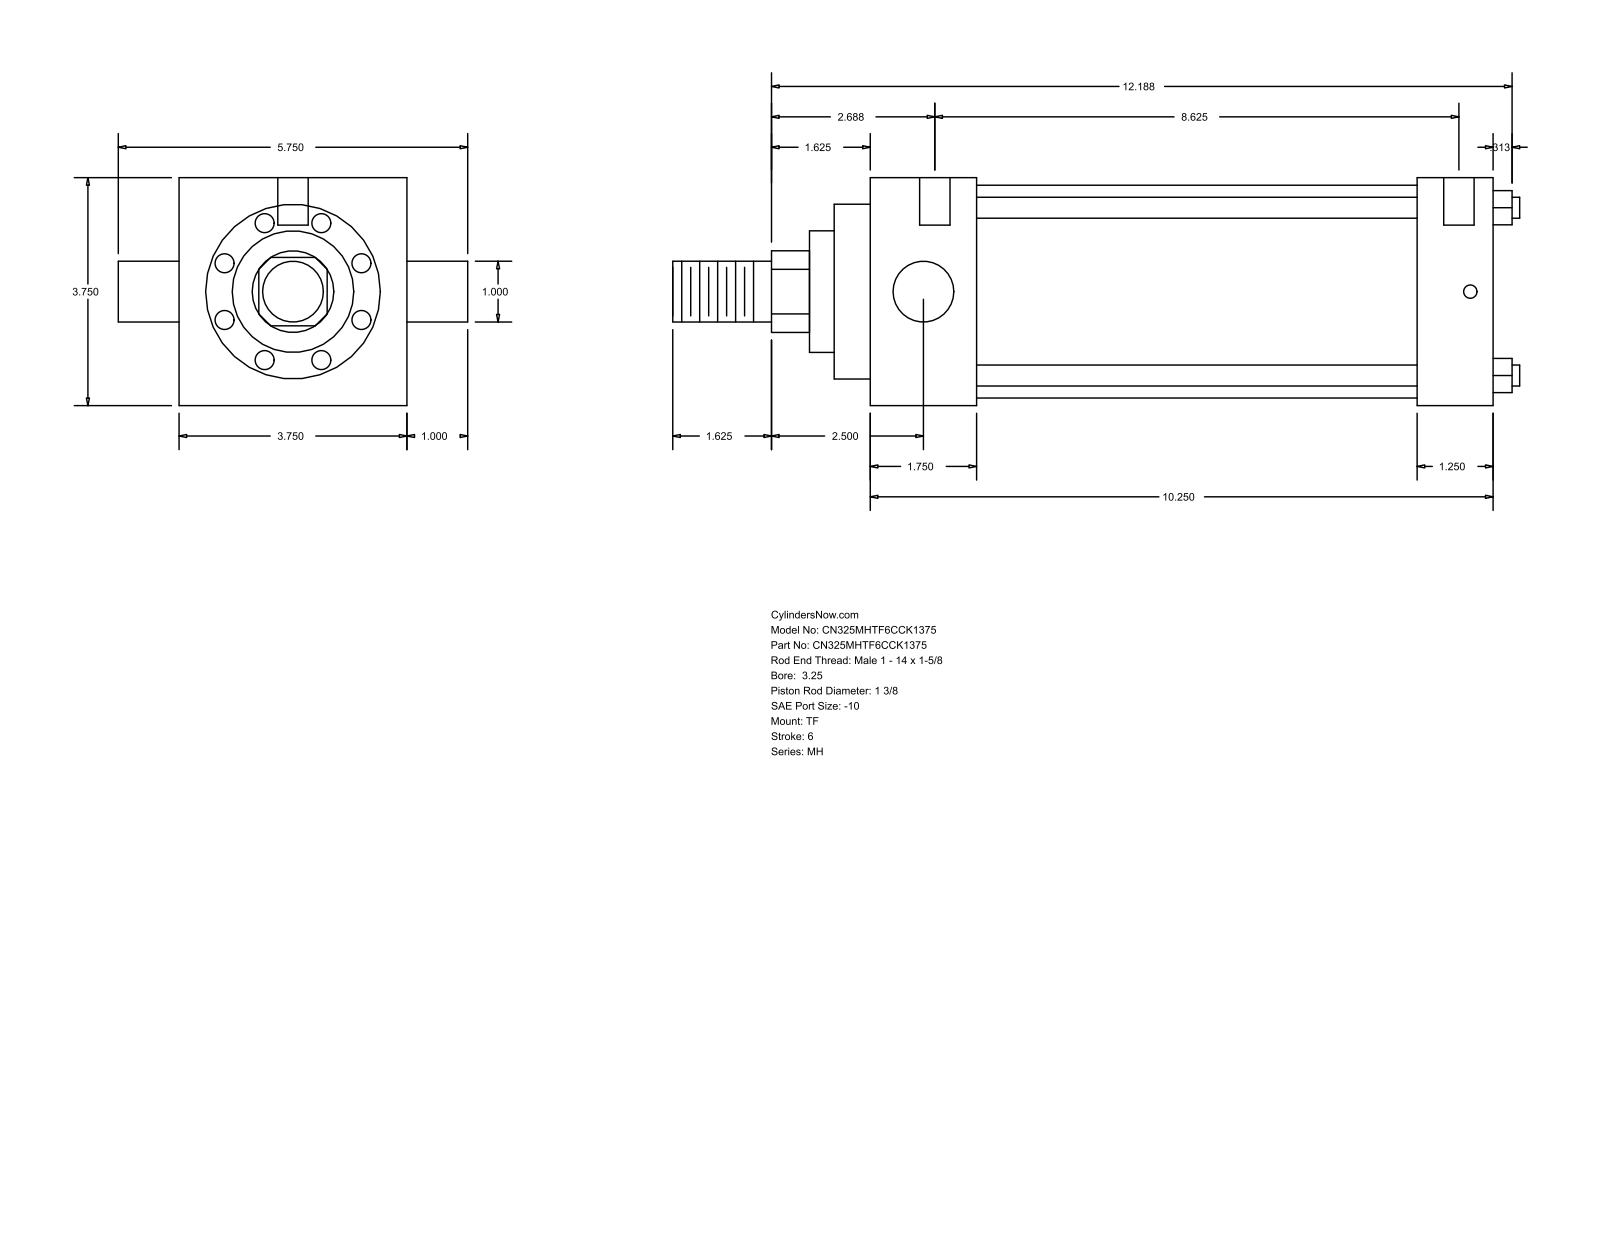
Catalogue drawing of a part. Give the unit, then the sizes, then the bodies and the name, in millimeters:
Units: millimetres
Overall size (bounding box): 354.01 × 146.05 × 95.25
Round holes (diameter × count): ⌀5.56 ×3, ⌀12.7 ×2
Round bosses / shafts (diameter × count): ⌀8.76 ×4, ⌀25.4 ×2, ⌀88.9 ×1, ⌀73.03 ×1, ⌀50.8 ×1, ⌀34.92 ×1
Partial cylindrical surfaces — rounded edges, fillets, slot ends (radius × count): R17.06 ×1
Main face-to-face distances: 95.24, 260.35, 44.45, 228.61, 184.16, 215.9, 31.74, 15.08, 59.53, 243.69
Hole centre spacings: 1.59, 4.76, 219.08, 220.67, 223.84, 225.43
Bodies: 0 solids, 86 faces (61 planar, 25 cylindrical, 0 other)
Part name (STEP PRODUCT): MH_TF__0325_1.375
STEP written by: GSSL Pune (CONFIG_CONTROL_DESIGN)
